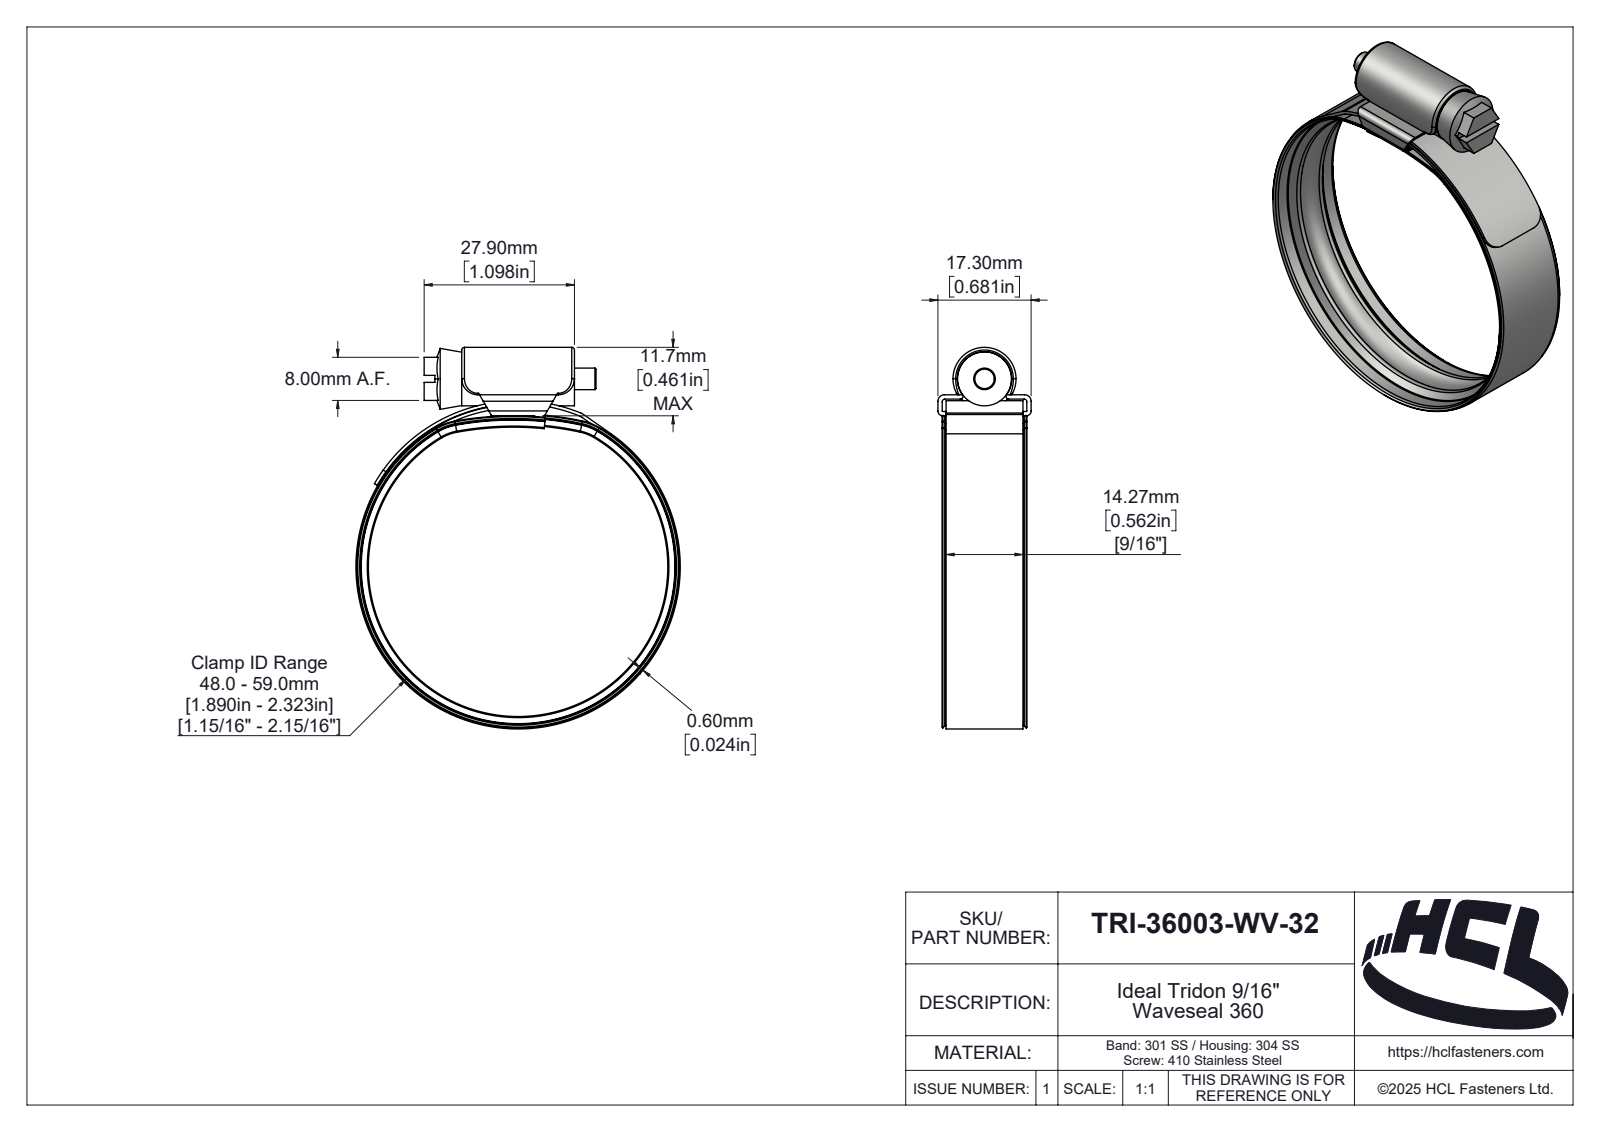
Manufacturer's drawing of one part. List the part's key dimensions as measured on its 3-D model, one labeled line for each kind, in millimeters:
Part name (STEP PRODUCT): TRI-36003-WV-32
STEP written by: SolidWorks 2025 (AUTOMOTIVE_DESIGN)
Units: millimetres
Bodies: 4 solids, 418 faces (42 planar, 119 cylindrical, 257 other)
Overall size (bounding box): 70.8 × 60.2 × 17.3
Volume: 5 402 mm³ · Surface area: 16 165 mm²
Round holes (diameter × count): ⌀58.4 ×1, ⌀59 ×1
Round bosses / shafts (diameter × count): ⌀60.2 ×1, ⌀58.8 ×1, ⌀10 ×1, ⌀4 ×1
Partial cylindrical surfaces — rounded edges, fillets, slot ends (radius × count): R0.5 ×6, R3 ×4, R0.1 ×2, R0.9 ×2, R1.2 ×2, R9.9 ×2, R10.1 ×2, R0.46 ×1
Main face-to-face distances: 0.8, 3.1, 14.26, 2.3, 0.6, 3.9, 27.9, 1.52, 15.78, 16.5
